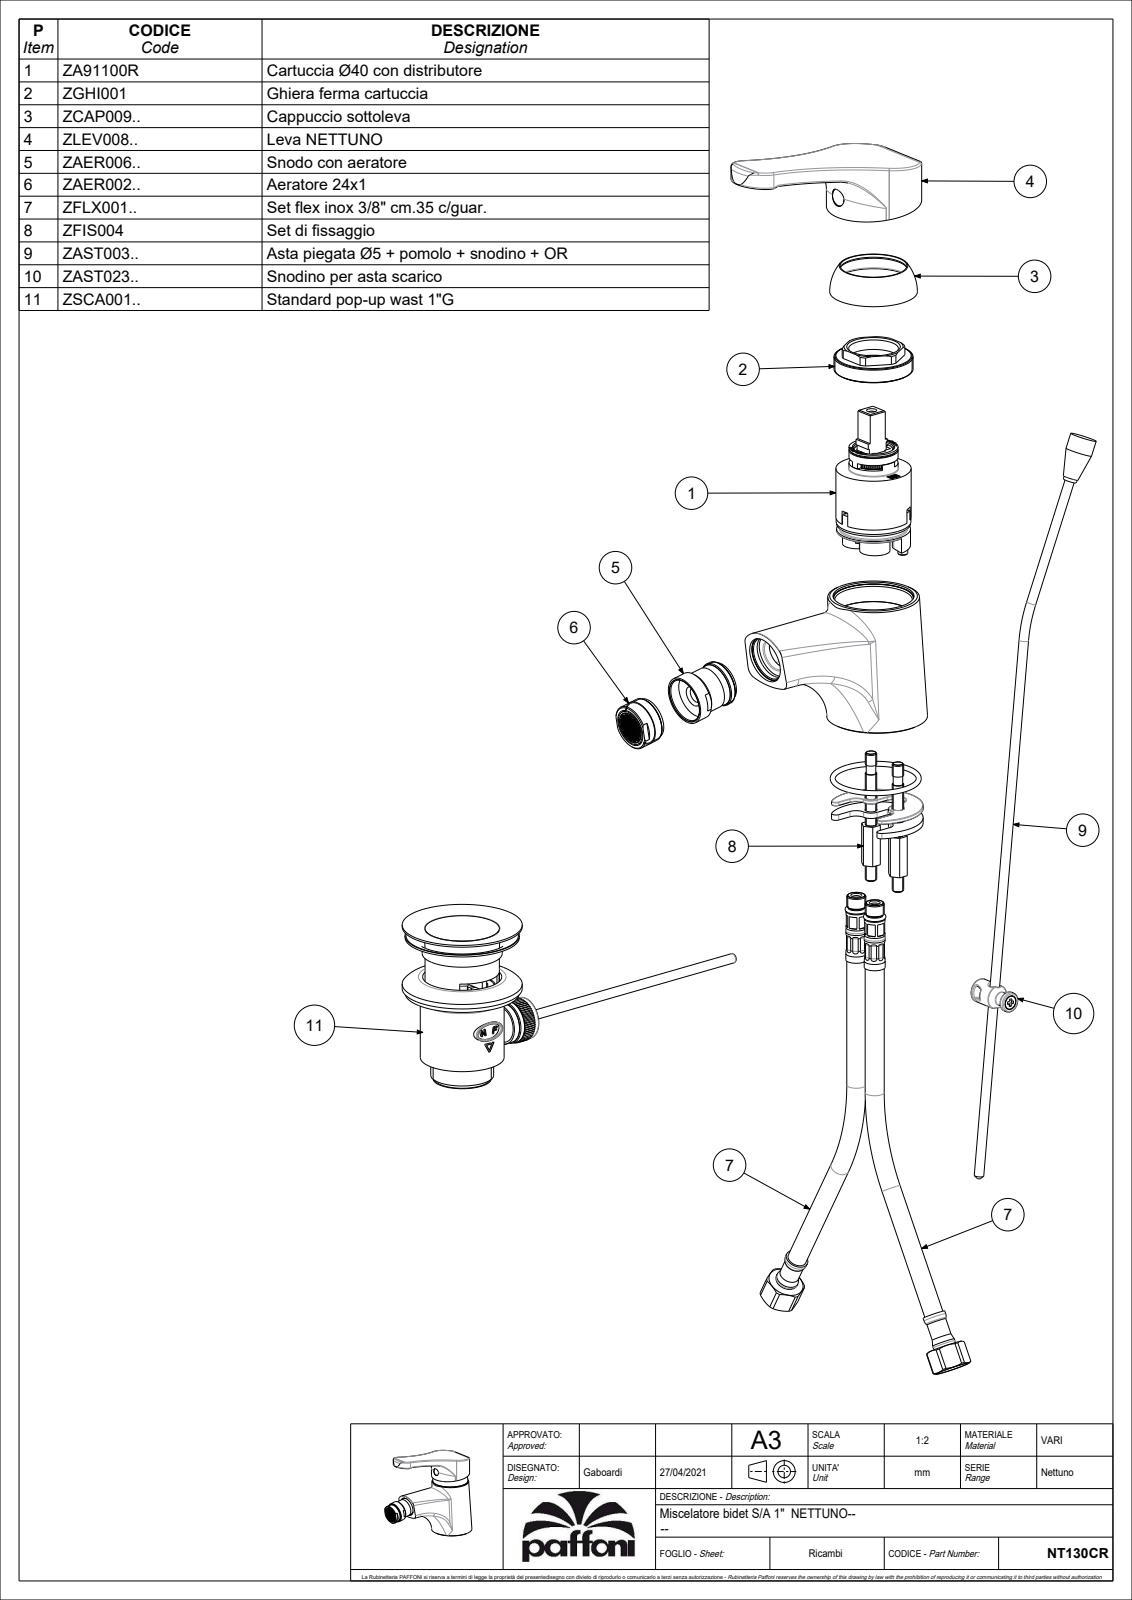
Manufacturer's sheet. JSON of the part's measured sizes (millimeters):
{"part_name": "NT135CR", "step_written_by": "CREO PARAMETRIC BY PTC INC, 2020044 (CONFIG_CONTROL_DESIGN)", "units": "millimeters", "bodies": {"solids": 4, "faces": 2827, "planar": 2044, "cylindrical": 417, "other": 366}, "overall_size": [151.33, 118.74, 52.89], "volume_mm3": 163344, "surface_area_mm2": 92508, "round_holes": [[8, 5], [11, 3], [4.6, 2], [5.25, 2], [7, 2], [9, 2], [12, 2], [21, 2], [3.3, 1], [4, 1], [4.5, 1], [5, 1]], "round_bosses_or_shafts": [[5, 4], [10, 3], [25.8, 2], [24, 2], [15.9, 2], [10.8, 2], [9.4, 2], [8.2, 2]], "partial_cylinders_radius": [[0.5, 51], [0.2, 24], [2, 9], [1, 5], [0.3, 4], [1.5, 4], [5, 3], [9, 3]], "face_to_face_distances": [3.7, 2, 1, 13, 5, 1.5, 3.5, 15, 4.5, 4], "hole_center_spacings": [13.12, 9.9, 0.71, 1.58, 2, 8.6, 8.81, 9.3]}
